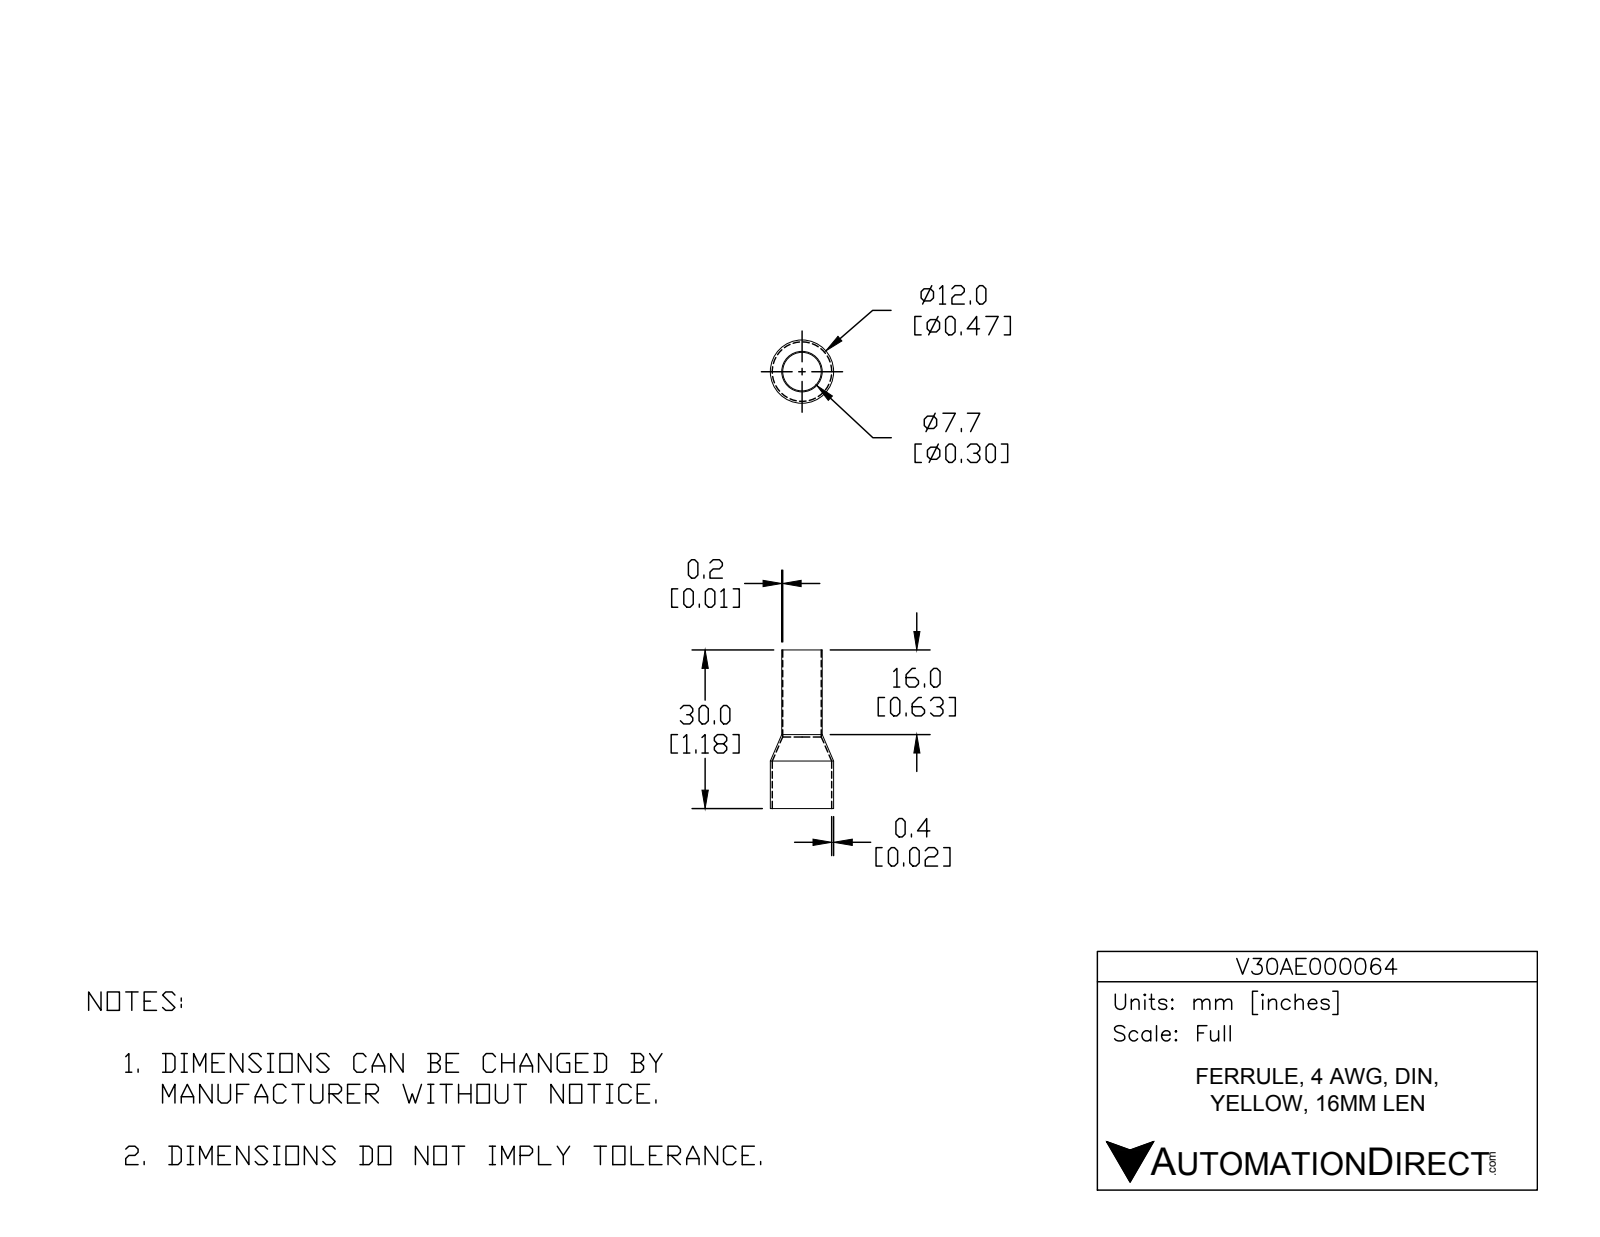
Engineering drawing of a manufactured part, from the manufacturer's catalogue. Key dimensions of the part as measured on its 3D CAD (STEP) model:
Part name (STEP PRODUCT): V30AE000064
STEP written by: SolidWorks 2017 (AUTOMOTIVE_DESIGN)
Units: millimetres
Bodies: 1 solid, 14 faces (2 planar, 8 cylindrical, 4 other)
Overall size (bounding box): 30 × 12 × 12
Volume: 265 mm³ · Surface area: 1 752 mm²
Round holes (diameter × count): ⌀7.3 ×1, ⌀11.2 ×1
Round bosses / shafts (diameter × count): ⌀12 ×1, ⌀7.7 ×1
Main face-to-face distances: 30
